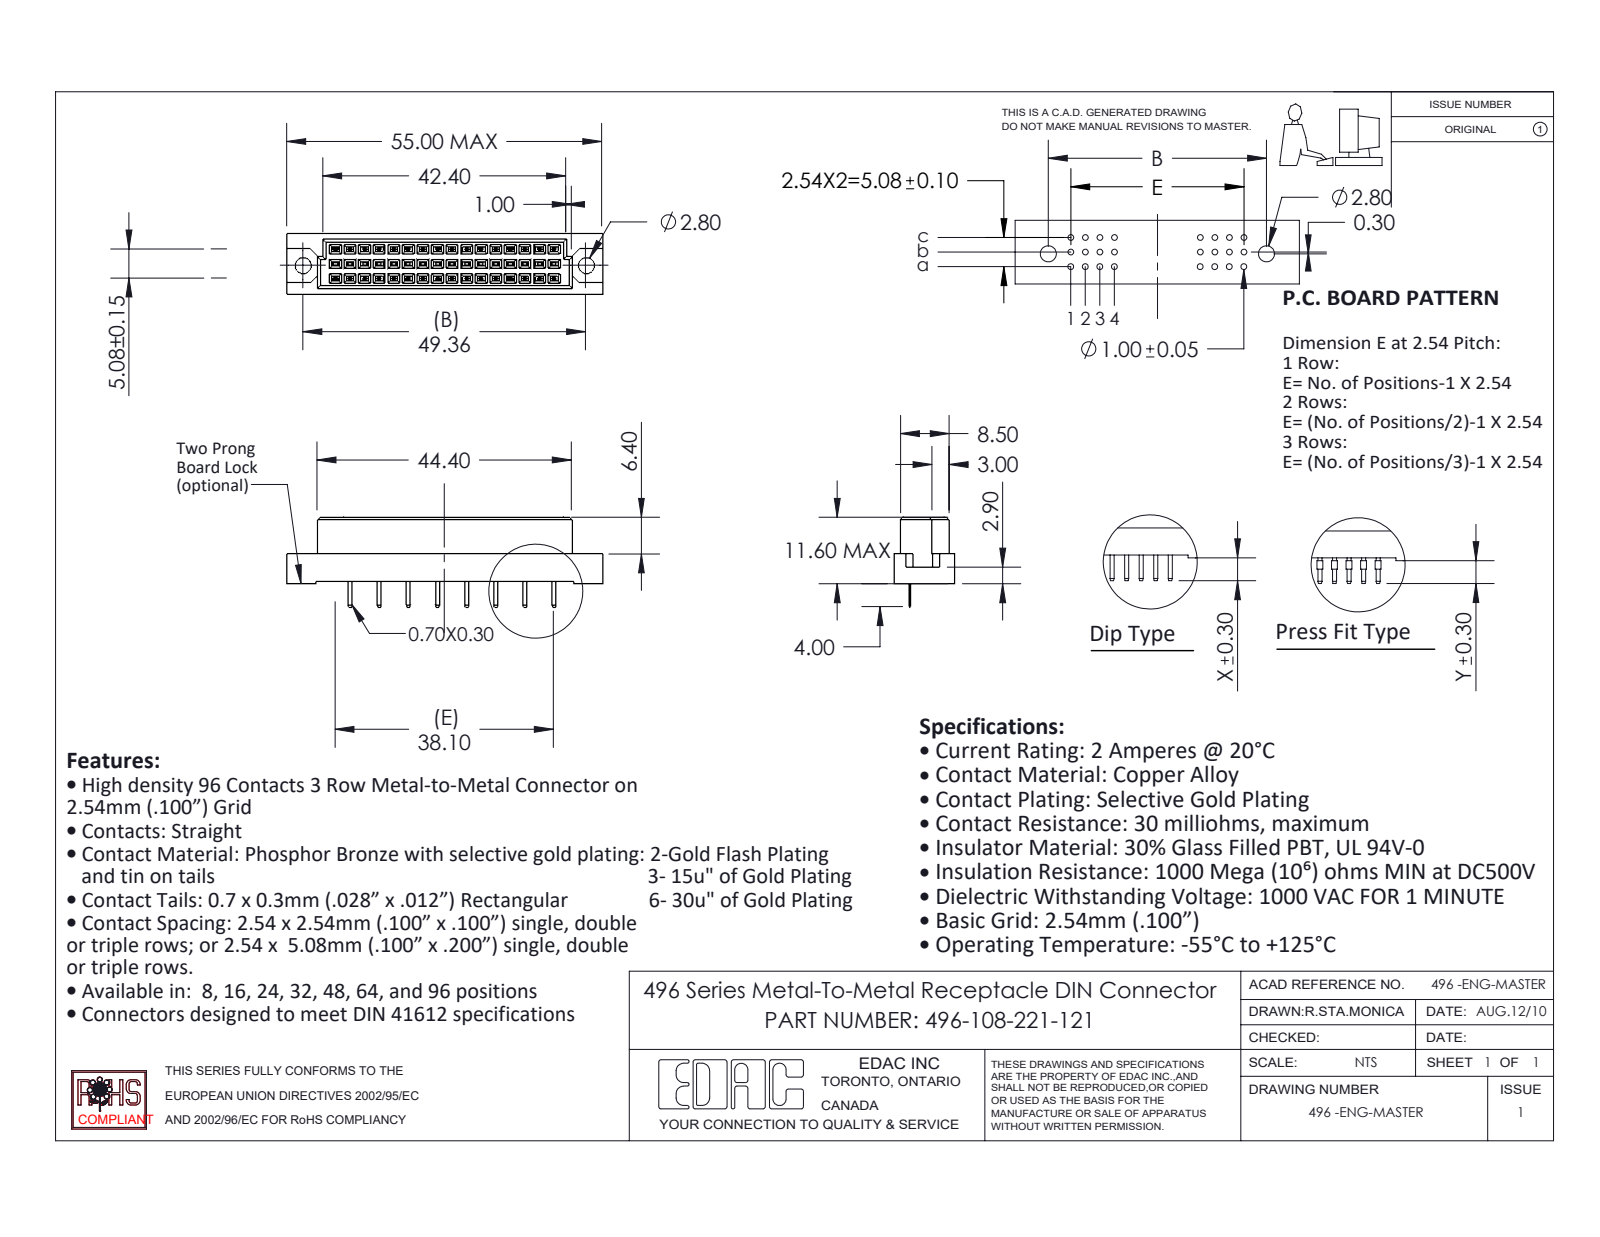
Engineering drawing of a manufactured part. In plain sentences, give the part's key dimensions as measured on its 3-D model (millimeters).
The part is named "496-290_21; 496 Part_48; 496-108-221-121". Its 3-D file was written by "SolidWorks 2020 (CONFIG_CONTROL_DESIGN)". It is 9 solids with 746 faces: 742 planar, 4 cylindrical and 0 other. Overall it measures 55 by 15.6 by 10.6 millimeters. Its volume is 4 604 cubic millimeters and its surface area 4 357 square millimeters. Round holes: 2 of diameter 2.8. The main face-to-face distances are 2.54, 5.08, 1.05, 9.55, 0.81, 10.6, 3.35, 1.73, 8.5, 0.56. The hole center spacings are 49.36.
